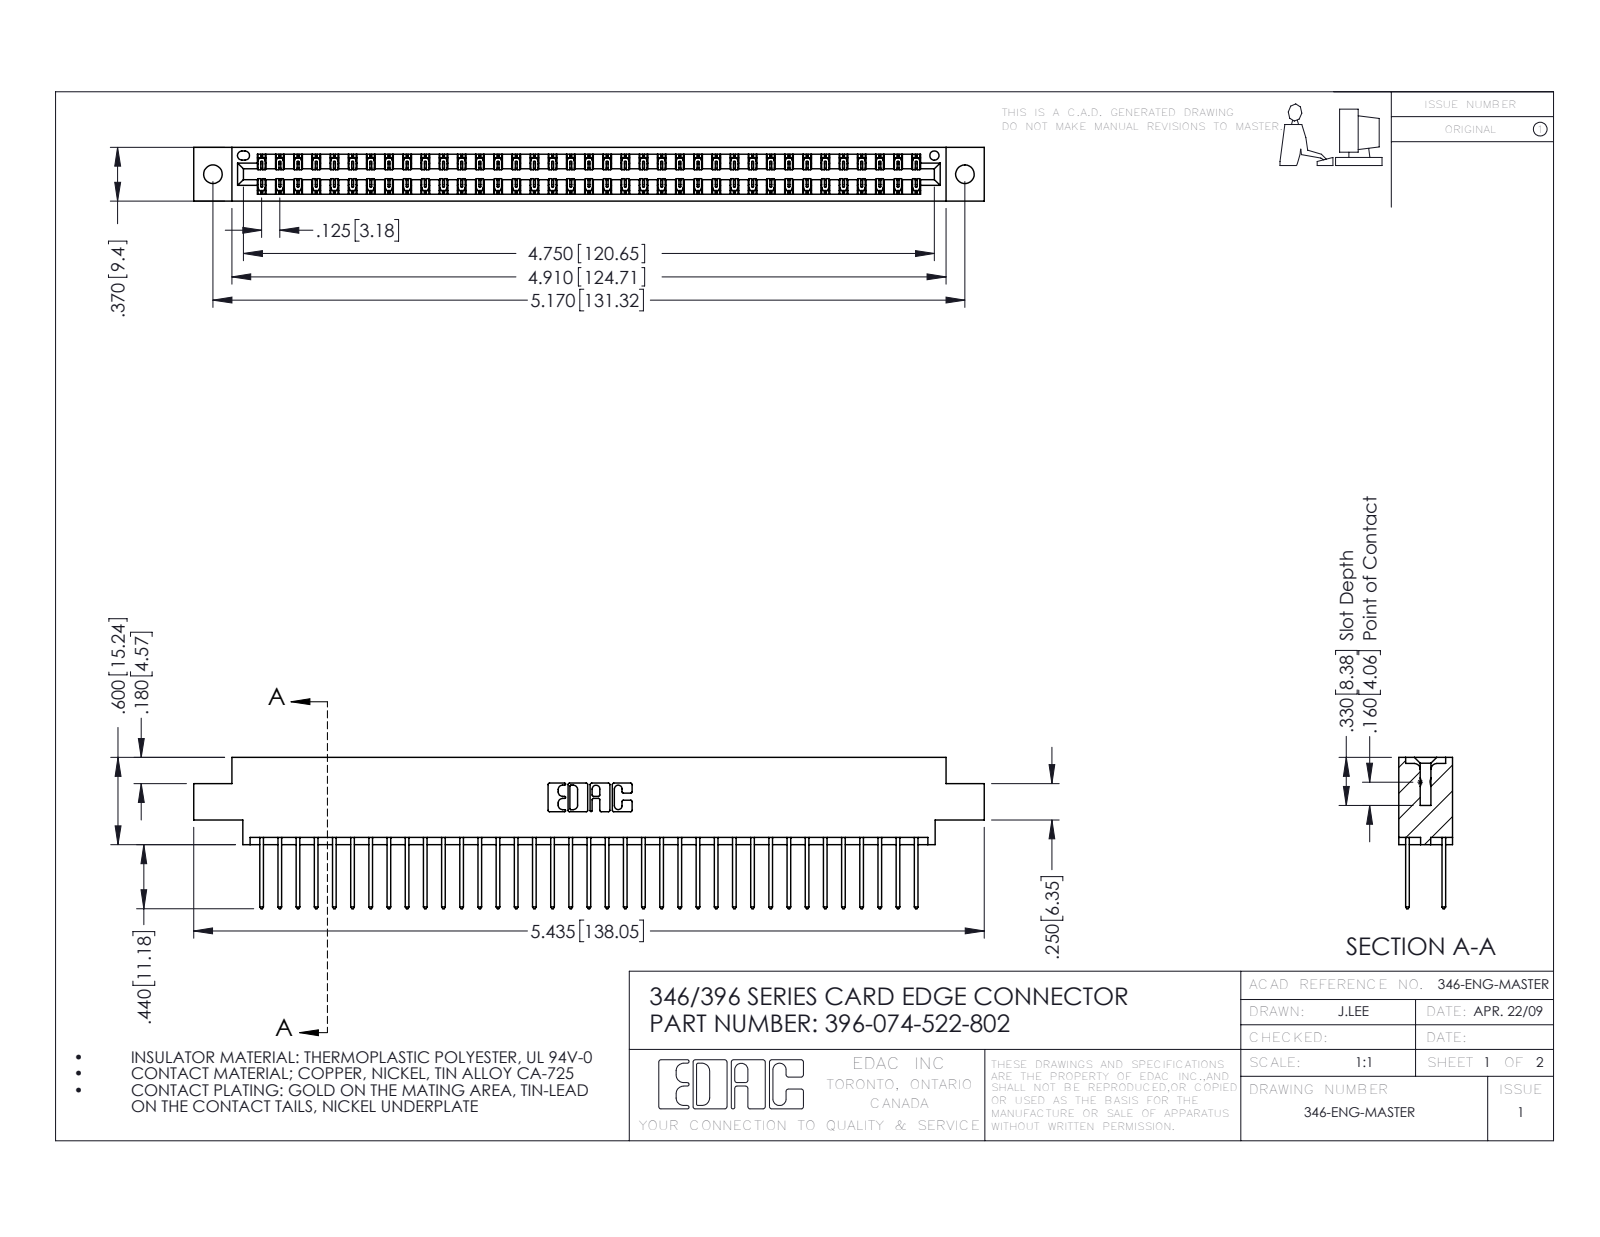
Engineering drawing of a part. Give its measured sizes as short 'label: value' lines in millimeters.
name: 396-074-522-802; 345-292-001_345-293-122; 346 Part_0.170 Offset - 0.128 Dia
written by: SolidWorks 2016 (CONFIG_CONTROL_DESIGN)
unit: mm
bodies: 75 solids, 3974 faces (2670 planar, 1304 cylindrical, 0 other)
size: 138 × 26.4 × 9.4
volume: 13 400 mm³; area: 19 160 mm²
holes: 2× ⌀3.3, 1× ⌀1.6
rounds: 111× R0.2, 74× R0.3, 22× R0.3, 6× R0.2, 6× R0.8, 3× R0.7, 2× R0.4, 2× R0.6
face distances: 1.2, 8.2, 6.4, 9.4, 1.8, 7.6, 0.6, 7, 3.8, 5.6
hole spacings: 6.2, 126, 131.3
